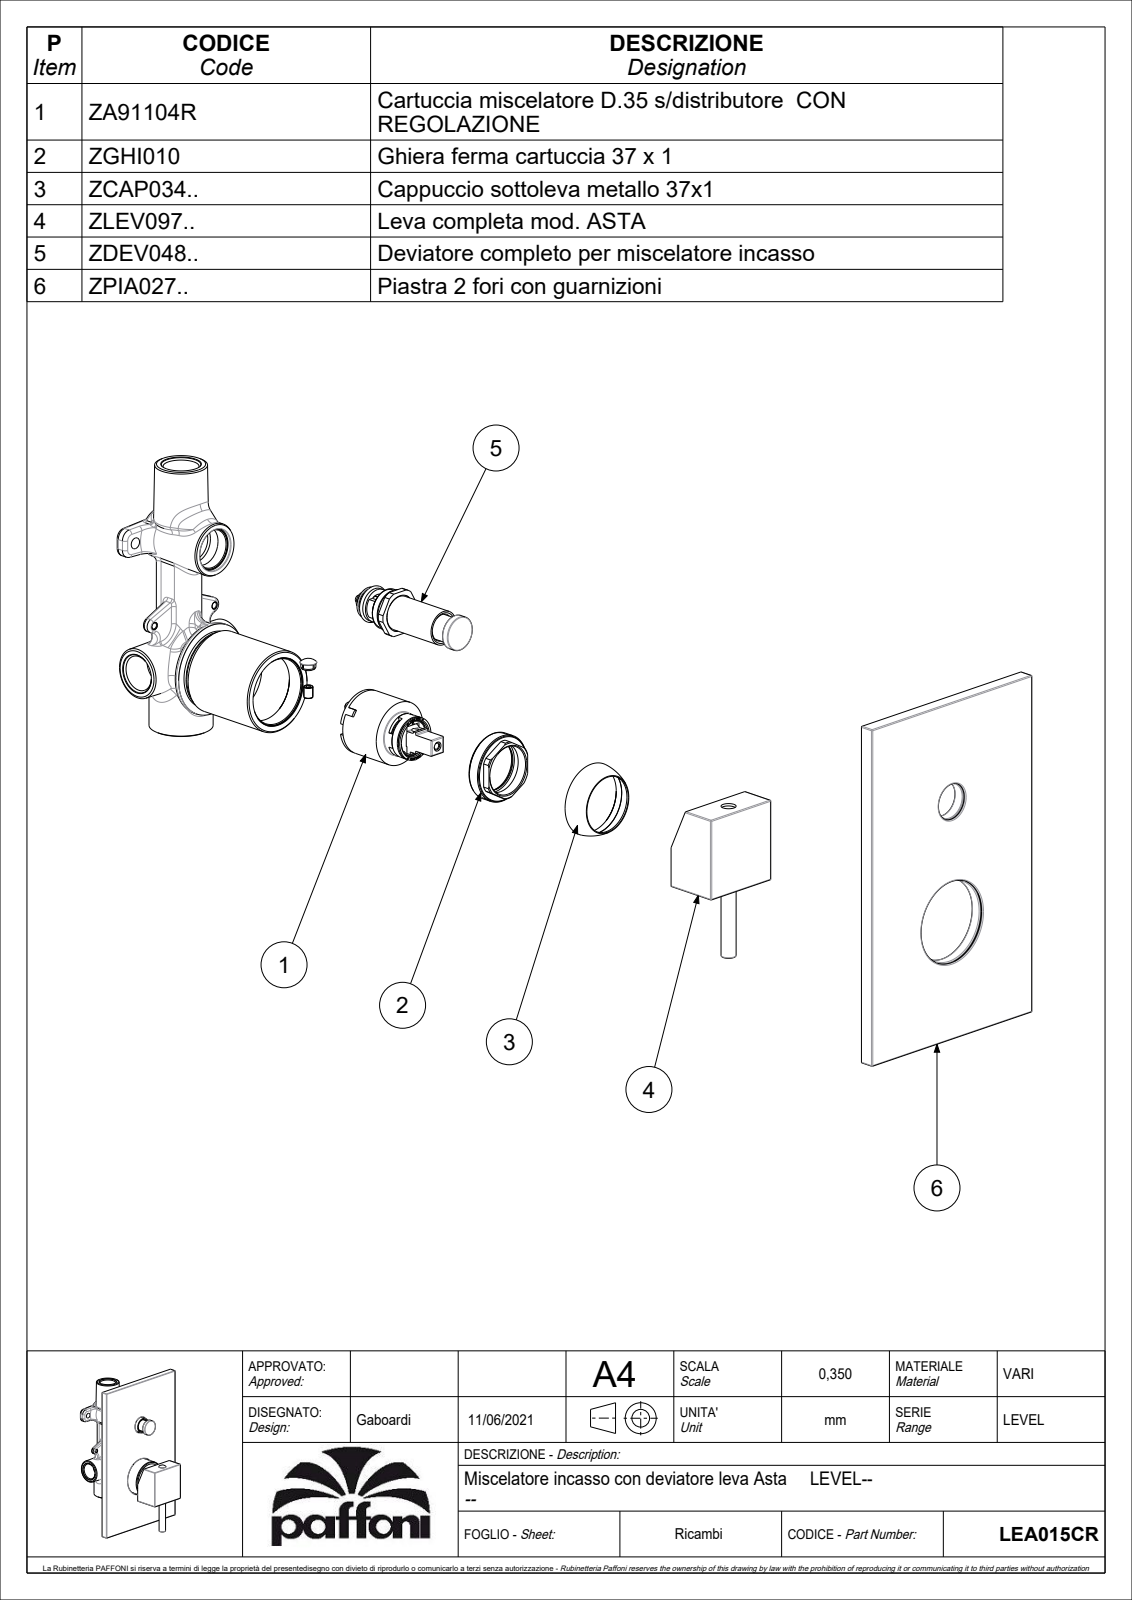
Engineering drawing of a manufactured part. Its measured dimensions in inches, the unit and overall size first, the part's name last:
Units: inches
Overall size (bounding box): 7.48 × 4.724 × 2.167
Round holes (diameter × count): ⌀0.157 ×2, ⌀0.13 ×1, ⌀0.197 ×1, ⌀0.217 ×1, ⌀0.236 ×1, ⌀0.319 ×1, ⌀0.413 ×1, ⌀0.583 ×1, ⌀0.756 ×1, ⌀0.768 ×1, ⌀0.783 ×1, ⌀0.787 ×1
Round bosses / shafts (diameter × count): ⌀2.008 ×1, ⌀1.929 ×1, ⌀1.764 ×1, ⌀1.378 ×1, ⌀0.984 ×1, ⌀0.925 ×1, ⌀0.921 ×1, ⌀0.906 ×1
Partial cylindrical surfaces — rounded edges, fillets, slot ends (radius × count): R0.02 ×24, R0.006 ×11, R0.039 ×10, R0.012 ×4, R0.276 ×1, R0.366 ×1, R0.427 ×1, R0.443 ×1
Main face-to-face distances: 0.098, 0.217, 0.315, 0.02, 0.118, 0.197, 1.843, 0.886, 1.476, 3.248
Hole centre spacings: 0.575, 2.677
Volume: 9.796 in³ · Surface area: 179 in²
Bodies: 5 solids, 987 faces (600 planar, 228 cylindrical, 159 other)
Part name (STEP PRODUCT): LEA015CR
STEP written by: CREO PARAMETRIC BY PTC INC, 2020044 (CONFIG_CONTROL_DESIGN)
